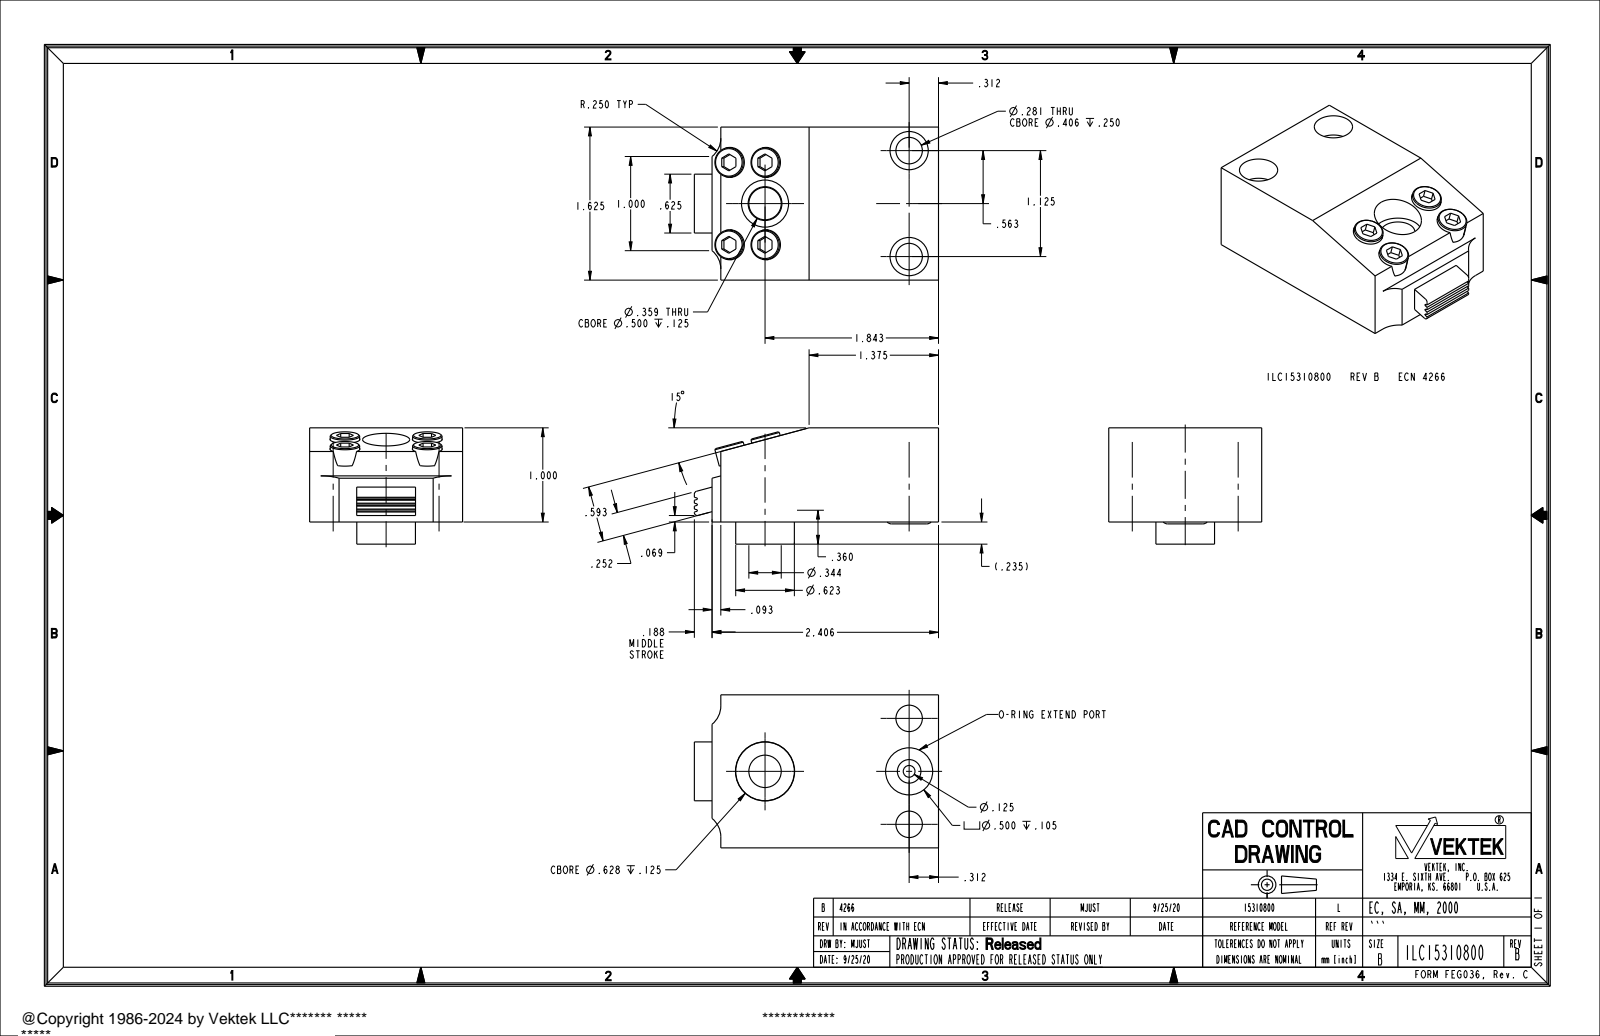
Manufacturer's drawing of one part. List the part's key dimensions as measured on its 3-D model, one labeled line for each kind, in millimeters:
Part name (STEP PRODUCT): ILC15310800
STEP written by: PRO/ENGINEER BY PARAMETRIC TECHNOLOGY CORPORATION, 2017170 (AUTOMOTIVE_DESIGN)
Units: millimetres
Bodies: 2 solids, 124 faces (72 planar, 40 cylindrical, 12 other)
Overall size (bounding box): 65.9 × 41.3 × 31.4
Volume: 56 190 mm³ · Surface area: 13 740 mm²
Round holes (diameter × count): ⌀8.1 ×4, ⌀7.1 ×2, ⌀10.3 ×2, ⌀12.7 ×2, ⌀3.2 ×1, ⌀8.7 ×1, ⌀9.1 ×1, ⌀16 ×1
Round bosses / shafts (diameter × count): ⌀7.9 ×4, ⌀15.8 ×1
Partial cylindrical surfaces — rounded edges, fillets, slot ends (radius × count): R0.8 ×2, R6.4 ×2
Main face-to-face distances: 41.3, 25.4, 58.8, 2.4, 61.1, 6.4, 6, 31.4, 8.6, 2.7
Hole centre spacings: 10.1, 14.3, 22.2, 24.4, 41.4, 28.6, 38.9
